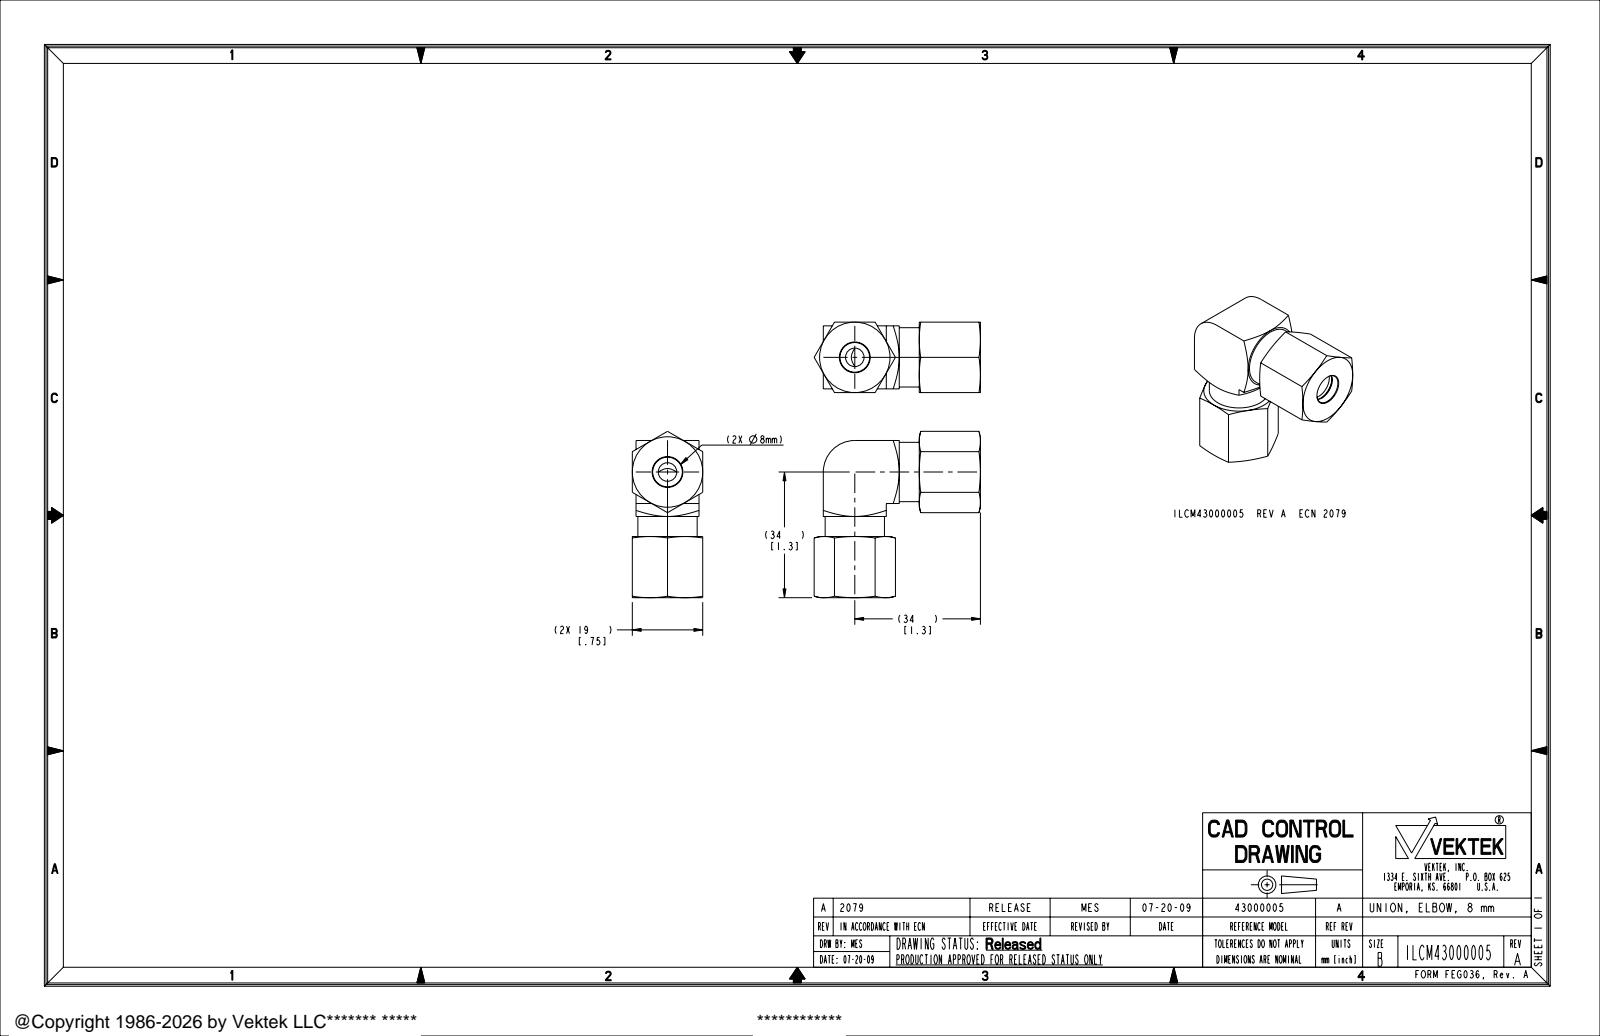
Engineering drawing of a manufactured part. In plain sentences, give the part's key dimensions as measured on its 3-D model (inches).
The part is named "ILCM43000005". Its 3-D file was written by "PRO/ENGINEER BY PARAMETRIC TECHNOLOGY CORPORATION, 2007460 (AUTOMOTIVE_DESIGN_CC2)". It is 1 solid with 133 faces: 34 planar, 33 cylindrical and 66 other. Overall it measures 1.767 by 1.767 by 0.748 inches. Its volume is 0.969 cubic inches and its surface area 12.07 square inches. Round holes: 2 of diameter 0.197, 2 of diameter 0.315, 2 of diameter 0.566. Round bosses or shafts: 2 of diameter 0.63, 2 of diameter 0.433, 2 of diameter 0.398. Partial cylindrical surfaces (rounded edges, fillets, slot ends): 1 of radius 0.335. The main face-to-face distances are 0.748, 0.039, 0.709, 0.669, 1.669, 1.02, 0.65, 1.28, 0.26, 0.39.
